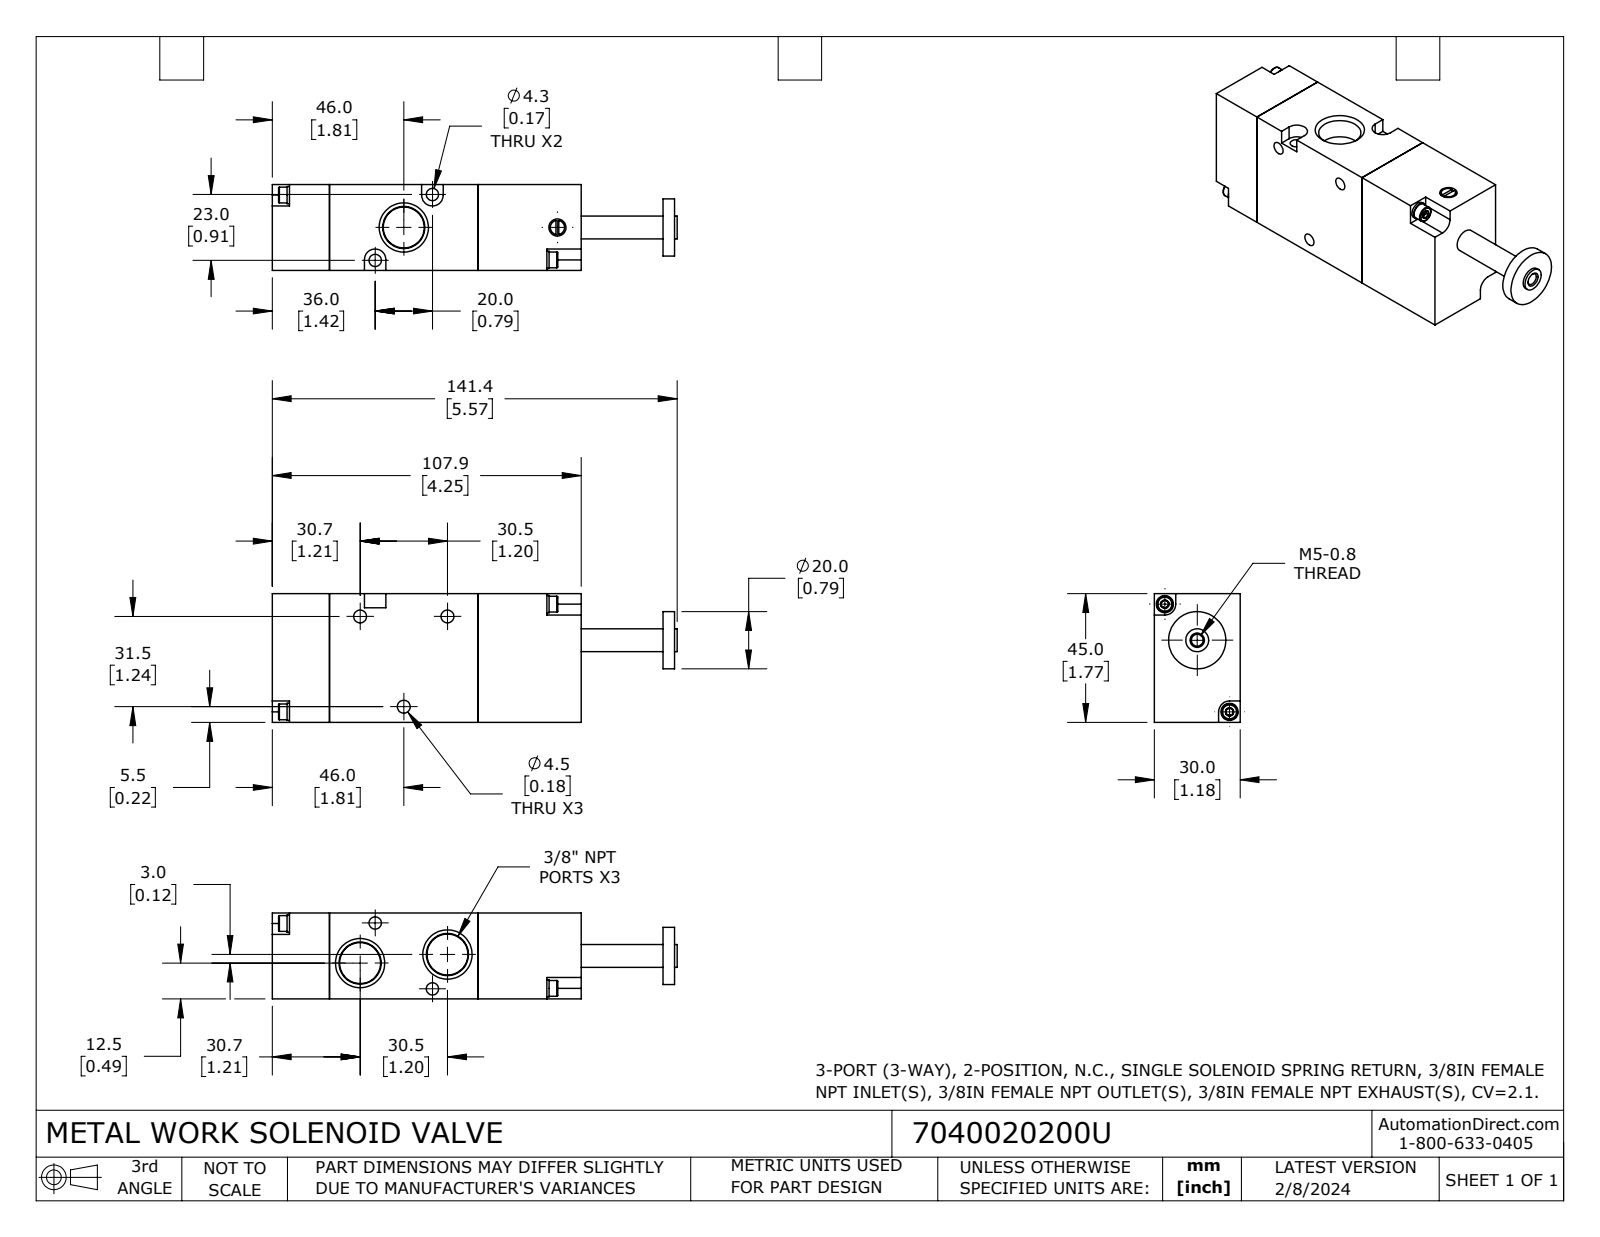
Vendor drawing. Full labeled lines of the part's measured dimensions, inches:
Part name (STEP PRODUCT): 7040020200U
STEP written by: SolidWorks 2023 (CONFIG_CONTROL_DESIGN)
Units: inches
Bodies: 11 solids, 247 faces (116 planar, 61 cylindrical, 70 other)
Overall size (bounding box): 5.567 × 1.772 × 1.181
Volume: 8.535 in³ · Surface area: 46.94 in²
Round holes (diameter × count): ⌀0.118 ×4, ⌀0.177 ×3, ⌀0.169 ×2, ⌀0.163 ×1, ⌀0.236 ×1
Round bosses / shafts (diameter × count): ⌀0.236 ×4, ⌀0.217 ×4, ⌀0.787 ×1, ⌀0.315 ×1, ⌀0.197 ×1
Partial cylindrical surfaces — rounded edges, fillets, slot ends (radius × count): R0.15 ×4, R0.148 ×2
Main face-to-face distances: 1.181, 2.043, 1.772, 0.787, 2.831, 1.417, 4.248, 3.461, 1.457, 0.315
Hole centre spacings: 0.666, 0.89, 1.08, 1.378, 1.48, 1.727, 1.2, 1.201
